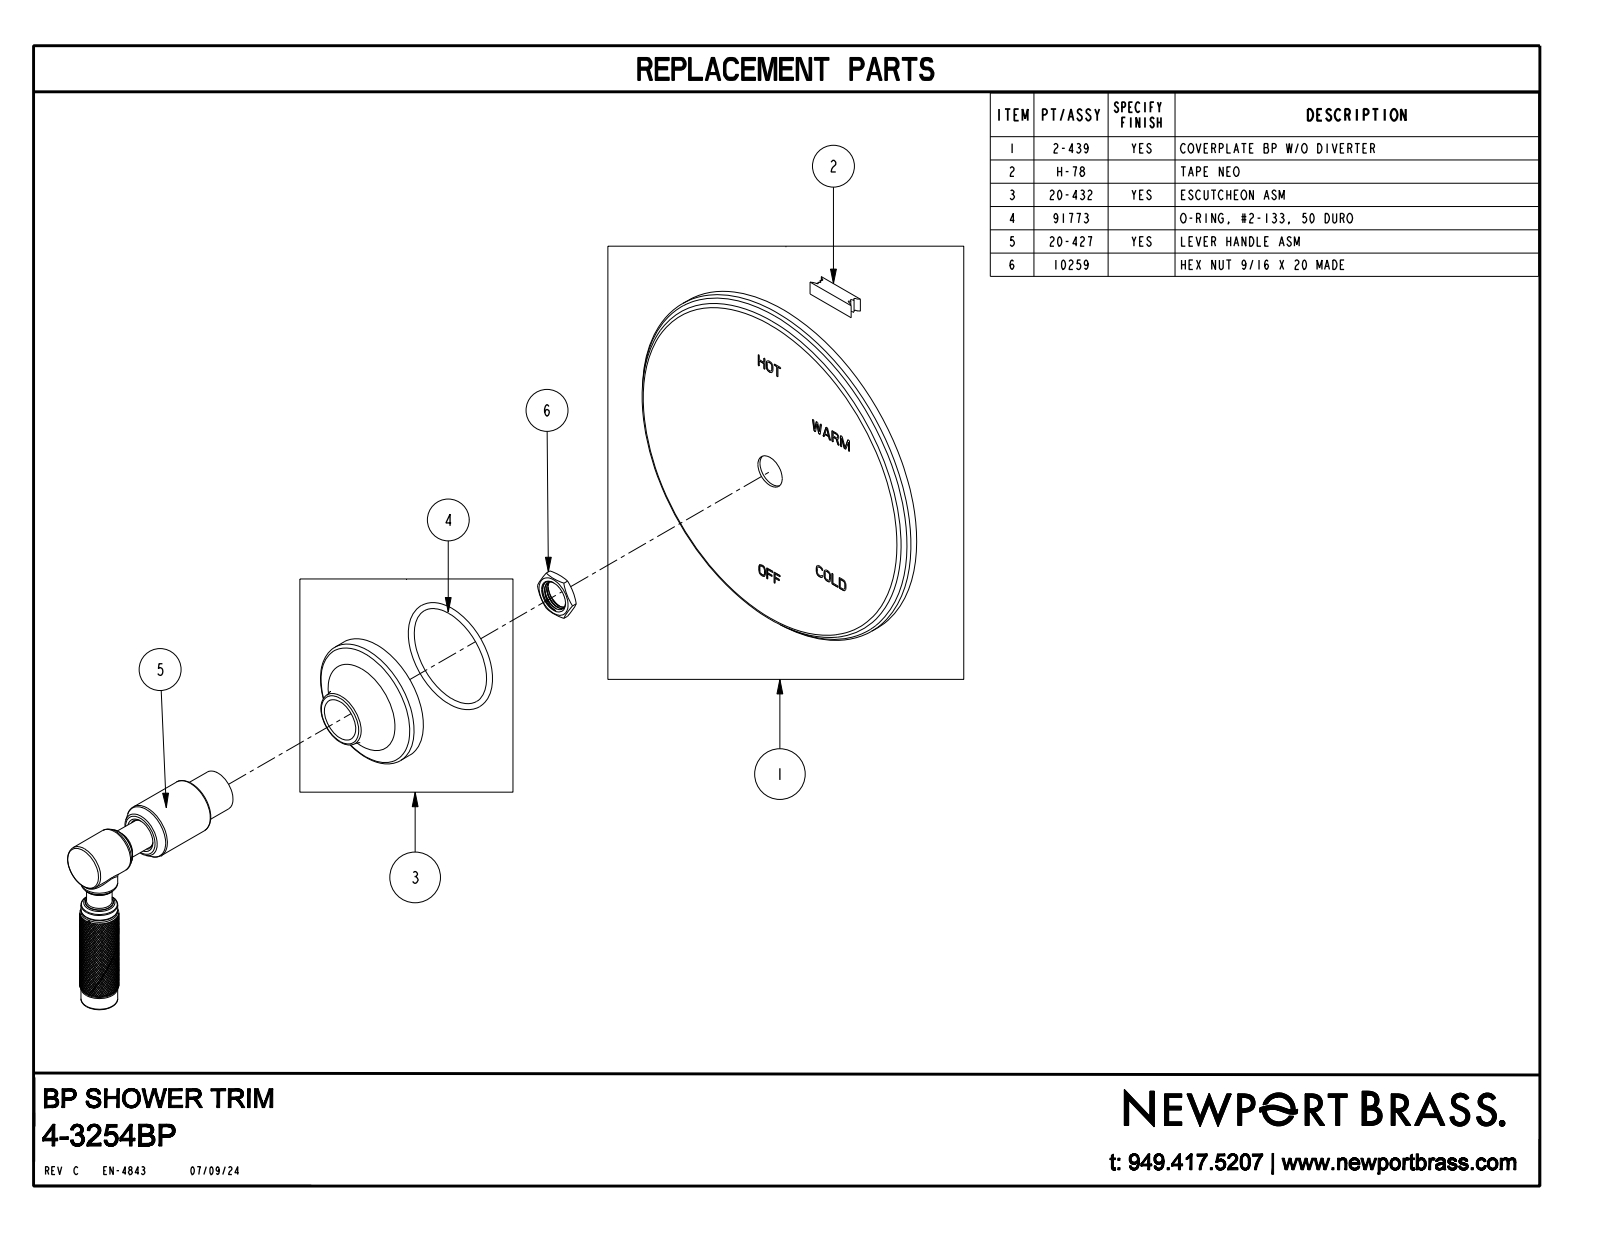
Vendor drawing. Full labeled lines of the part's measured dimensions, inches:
Part name (STEP PRODUCT): 4-3254BP
STEP written by: CREO PARAMETRIC BY PTC INC, 2023134 (CONFIG_CONTROL_DESIGN)
Units: inches
Bodies: 1 solid, 5501 faces (336 planar, 1009 cylindrical, 4156 other)
Overall size (bounding box): 6.5 × 6.5 × 3.967
Volume: 6.027 in³ · Surface area: 92.02 in²
Round holes (diameter × count): ⌀0.59 ×1, ⌀6.4 ×1
Round bosses / shafts (diameter × count): ⌀6.5 ×1, ⌀2.25 ×1, ⌀0.965 ×1, ⌀0.85 ×1, ⌀0.787 ×1, ⌀0.67 ×1, ⌀0.63 ×1, ⌀0.52 ×1
Main face-to-face distances: 0.05, 0.263, 0.313, 2.471, 2.208, 2.158, 0.309, 0.046, 2.161, 1.213
